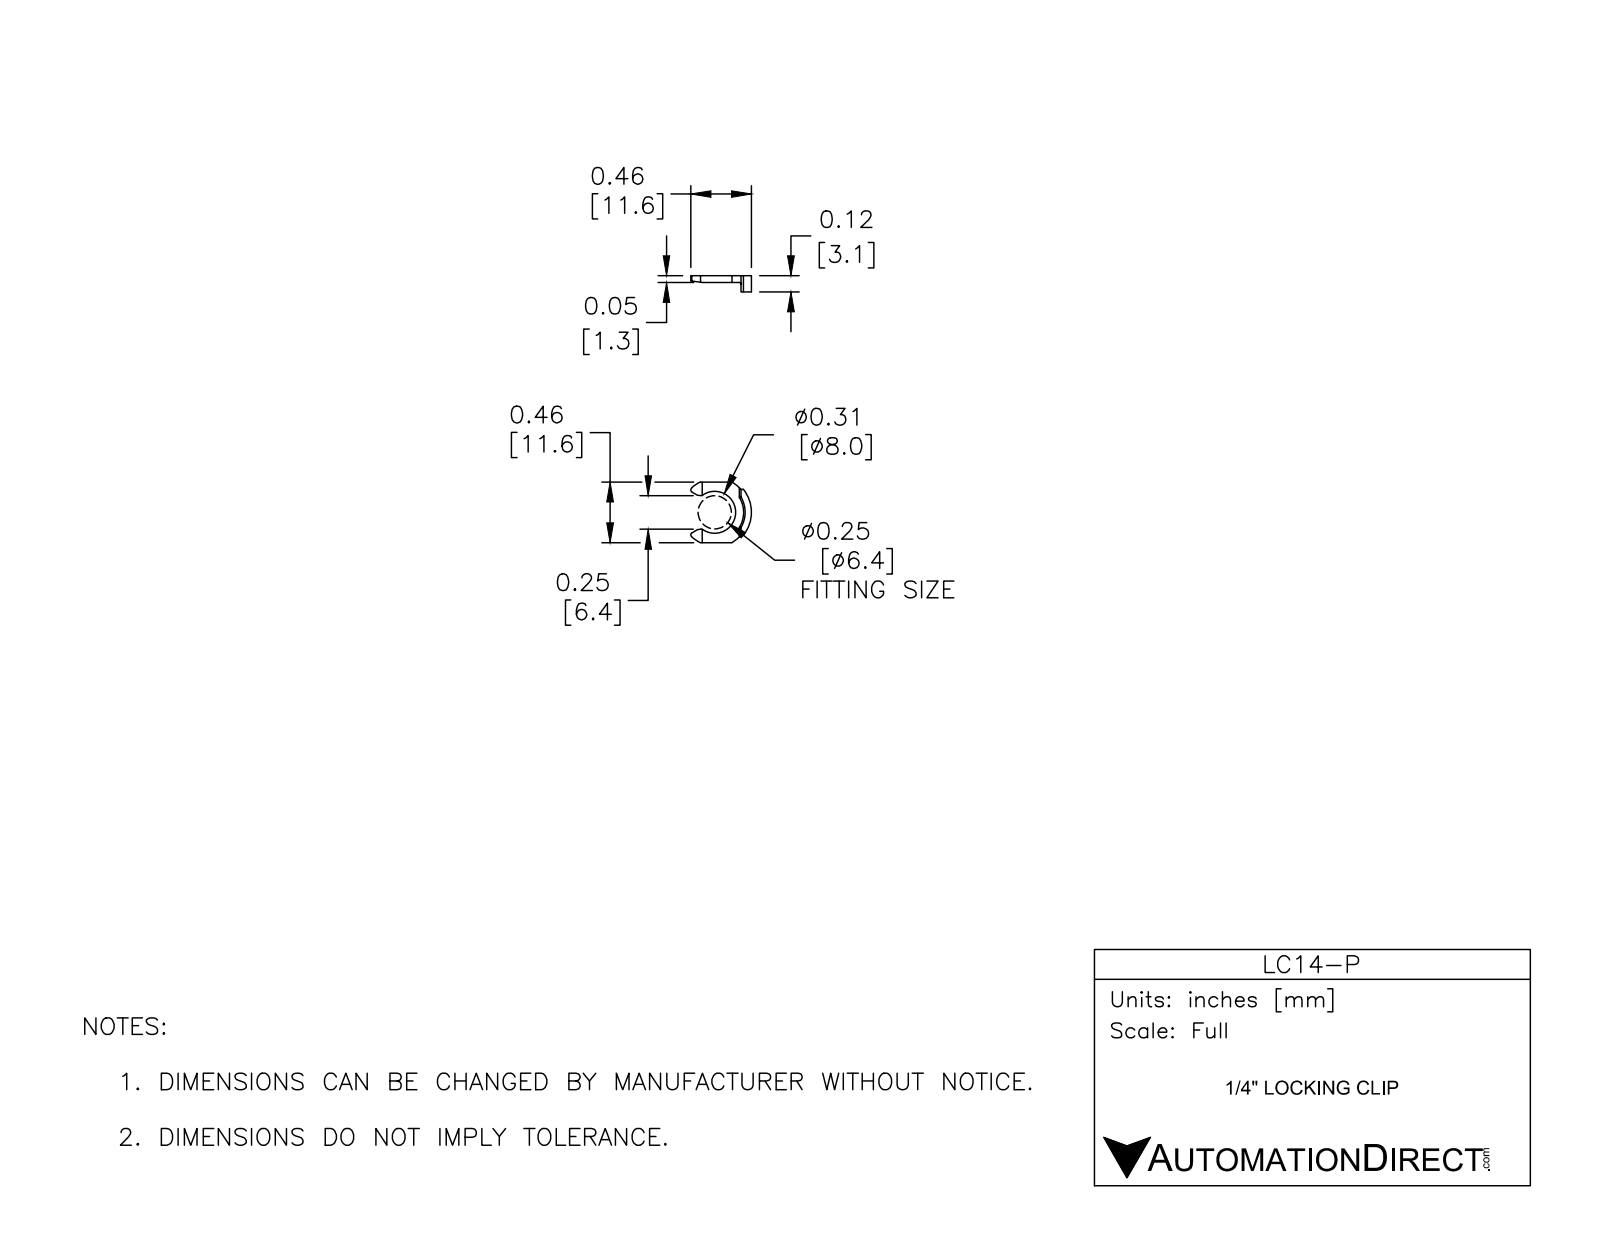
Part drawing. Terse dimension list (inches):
name: LC14-P
written by: SolidWorks 2017 (AUTOMOTIVE_DESIGN)
unit: in
bodies: 1 solid, 32 faces (15 planar, 16 cylindrical, 1 other)
size: 0.457 × 0.456 × 0.122
volume: 0.006 in³; area: 0.352 in²
rounds: 4× R0.02, 1× R0.012, 1× R0.157, 1× R0.228, 1× R0.253, 1× R0.262, 1× R0.276
face distances: 0.051, 0.122, 0.071, 0.457, 0.055, 0.402, 0.346
